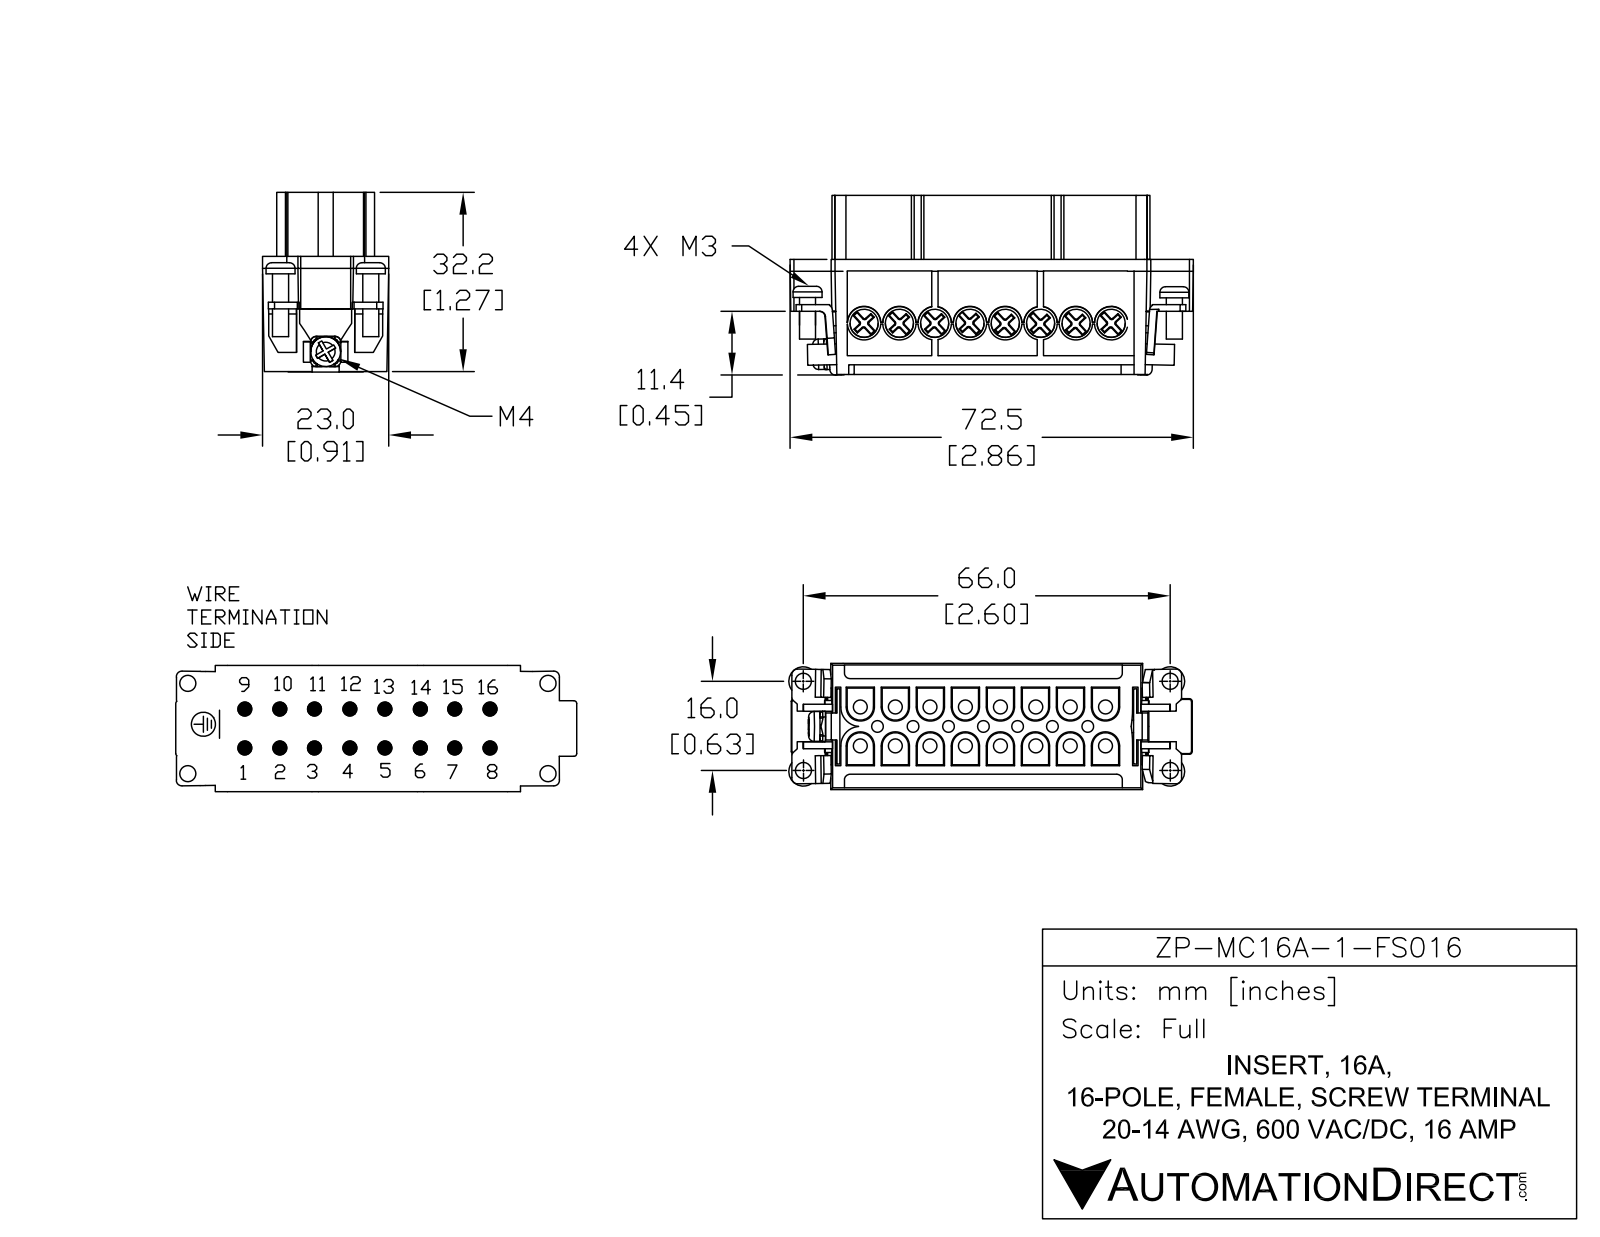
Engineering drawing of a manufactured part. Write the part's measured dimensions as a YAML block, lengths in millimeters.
part_name: "ZP-MC16A-1-FS016"
step_written_by: "SolidWorks 2014 (AUTOMOTIVE_DESIGN)"
units: millimeters
bodies: {solids: 1, faces: 1101, planar: 697, cylindrical: 270, other: 134}
overall_size: [72.5, 32.31, 22.7]
volume: 29251
surface_area: 17303
round_holes:
  - {diameter: 2.5, count: 16}
  - {diameter: 3, count: 16}
  - {diameter: 5.06, count: 8}
  - {diameter: 5.06, count: 8}
  - {diameter: 2.1, count: 7}
  - {diameter: 2.49, count: 1}
round_bosses_or_shafts:
  - {diameter: 6, count: 16}
  - {diameter: 5.44, count: 16}
  - {diameter: 5.21, count: 4}
  - {diameter: 2.89, count: 4}
  - {diameter: 5.38, count: 1}
partial_cylinders:
  - {radius: 0.5, count: 20}
  - {radius: 1, count: 20}
  - {radius: 2, count: 4}
  - {radius: 3.51, count: 2}
  - {radius: 22.59, count: 2}
face_to_face_distances: [6.3, 12.6, 15.1, 18.9, 25.2, 17.6, 11.51, 3, 18.1, 32.22]
hole_center_spacings: [7, 9.42, 6.3, 12.6, 14.41, 18.9, 20.15, 6.35]
